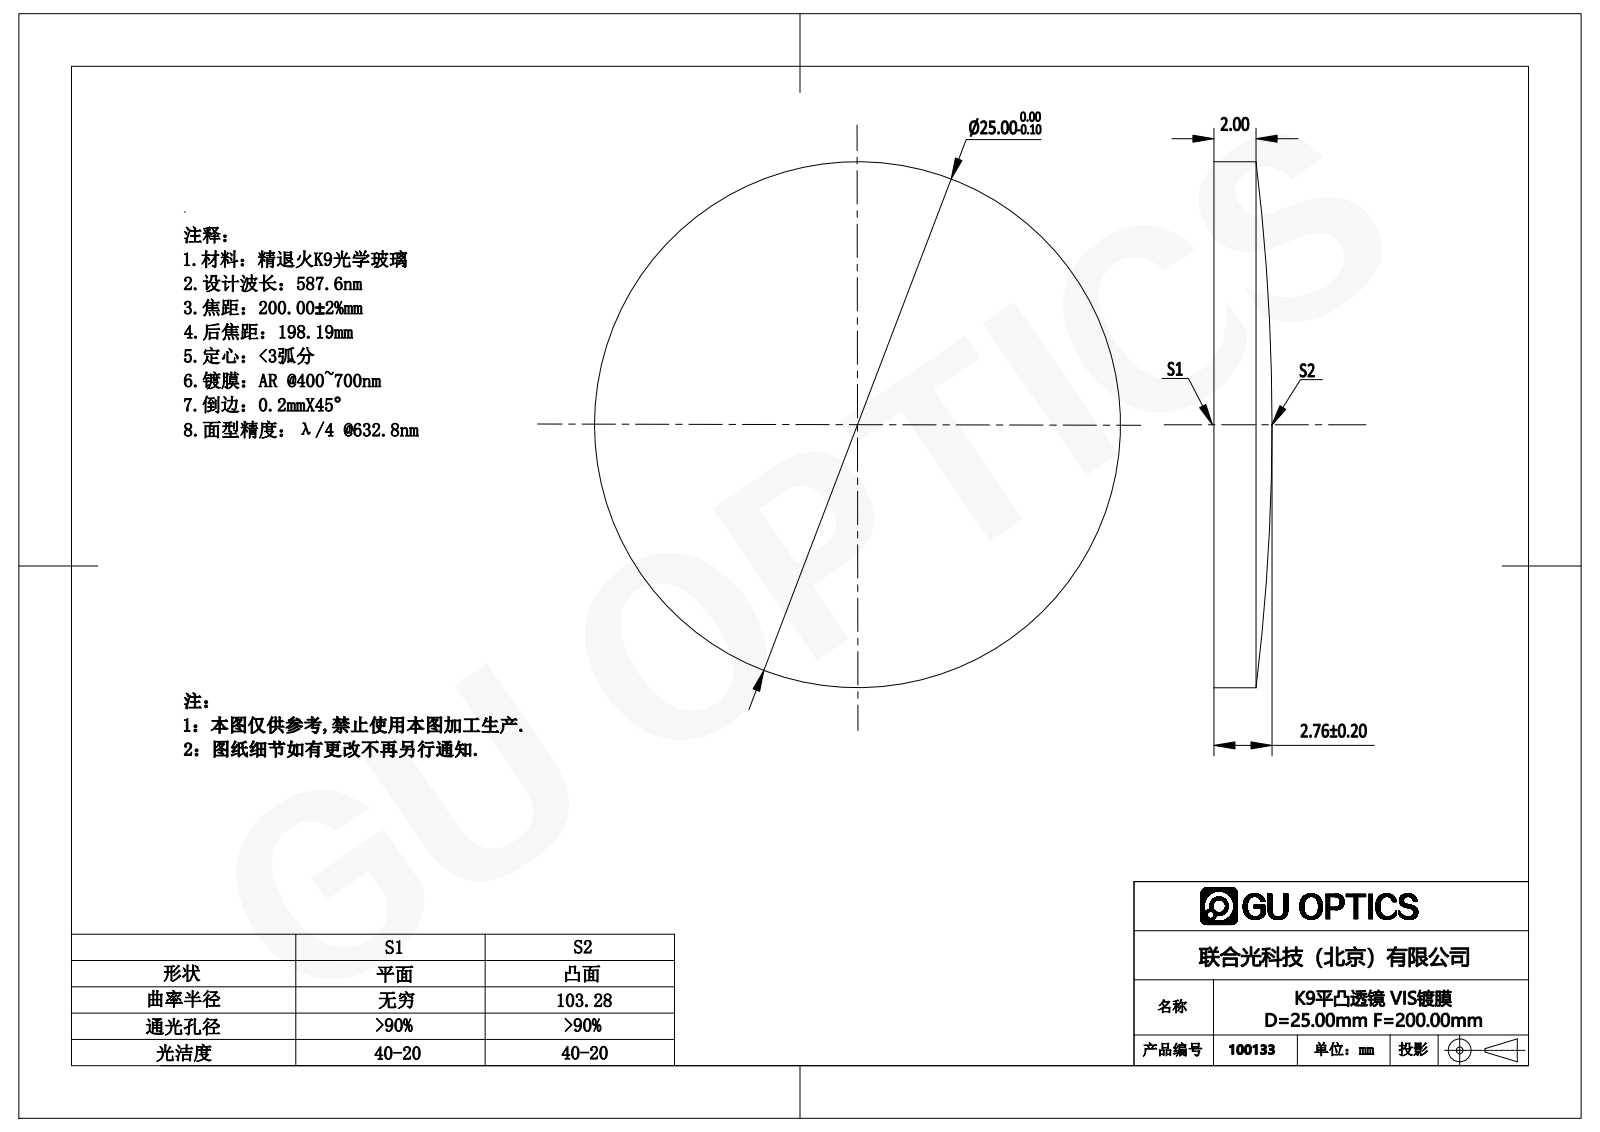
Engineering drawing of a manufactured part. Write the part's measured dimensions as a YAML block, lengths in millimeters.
part_name: "100133"
step_written_by: "SolidWorks 2016 (AUTOMOTIVE_DESIGN)"
units: millimeters
bodies: {solids: 1, faces: 5, planar: 1, cylindrical: 2, other: 2}
overall_size: [25, 25, 2.76]
volume: 1169
surface_area: 1141
round_bosses_or_shafts:
  - {diameter: 25, count: 1}
